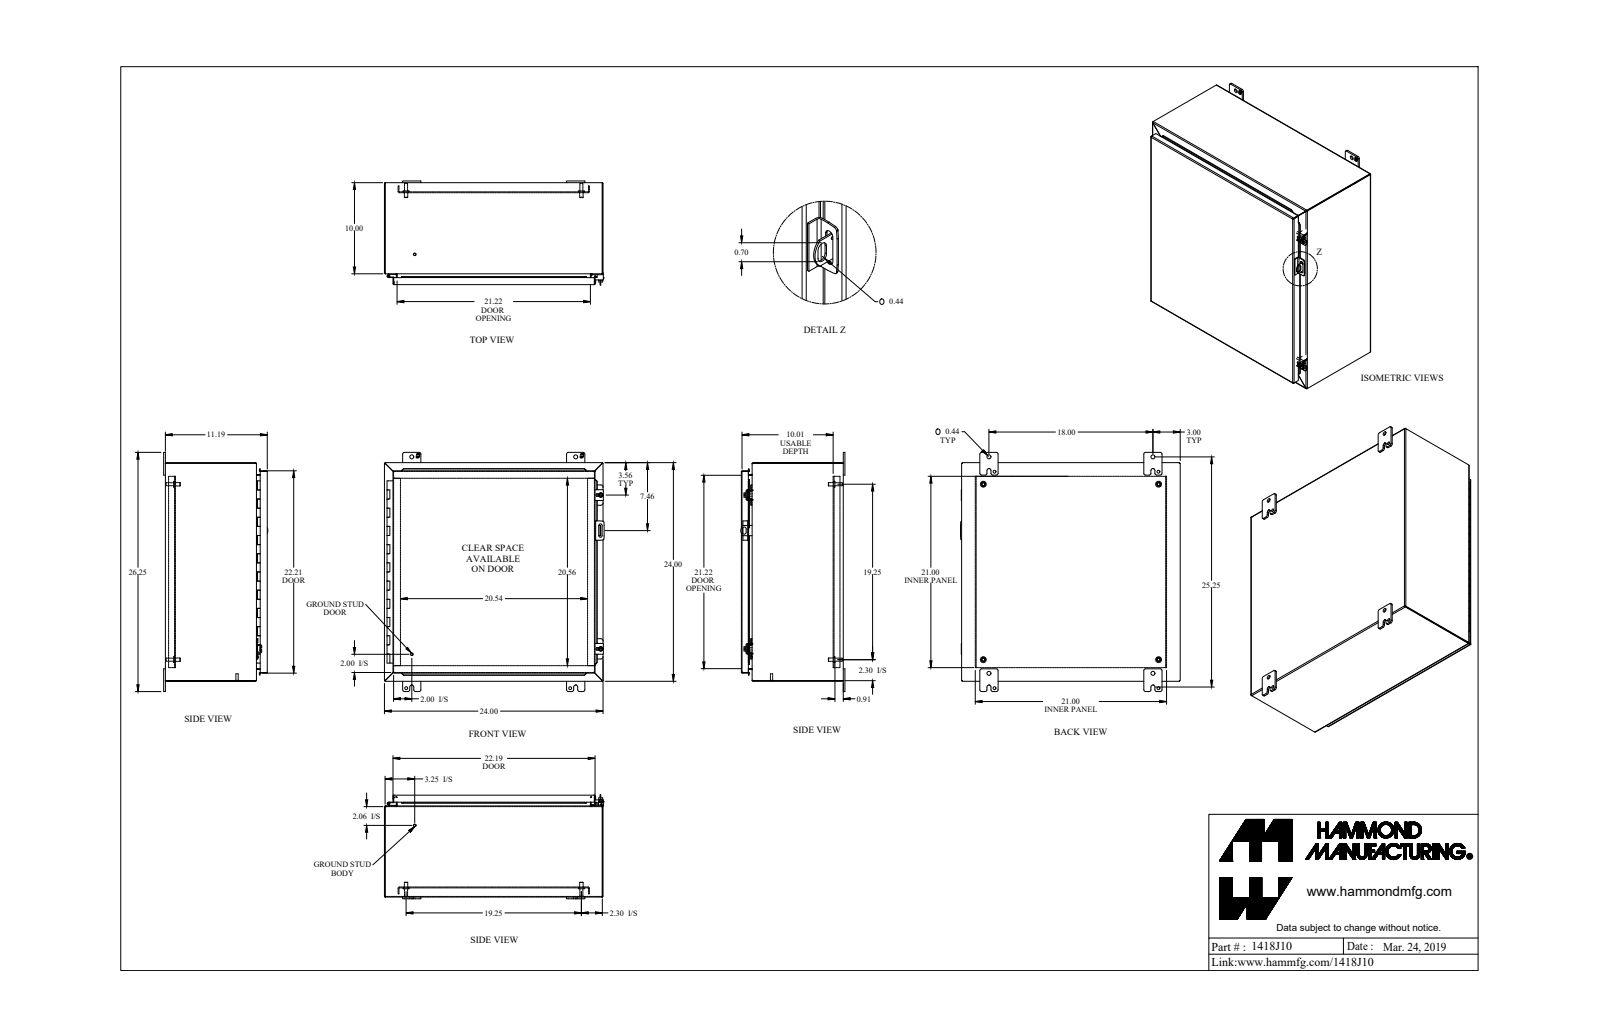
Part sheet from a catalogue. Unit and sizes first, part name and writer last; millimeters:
Units: millimetres
Overall size (bounding box): 666.8 × 612.8 × 290.5
Round holes (diameter × count): ⌀8 ×4, ⌀11.1 ×4, ⌀12.7 ×4, ⌀5.4 ×2, ⌀6.7 ×2, ⌀7.8 ×2, ⌀9.5 ×2, ⌀3.2 ×1, ⌀4.7 ×1, ⌀11.3 ×1, ⌀11.3 ×1
Round bosses / shafts (diameter × count): ⌀16.5 ×4, ⌀9.5 ×4, ⌀8.4 ×4, ⌀25.4 ×2, ⌀12.7 ×2, ⌀9.9 ×2, ⌀7.1 ×2, ⌀6.4 ×2
Partial cylindrical surfaces — rounded edges, fillets, slot ends (radius × count): R4.8 ×26, R0.9 ×20, R2.7 ×20, R1.2 ×13, R3.6 ×13, R1.1 ×8, R5.5 ×8, R6.4 ×8
Main face-to-face distances: 1.8, 282.3, 607.8, 280.4, 284.1, 23.8, 605.9, 609.6, 2.4, 25.6
Hole centre spacings: 489, 457.2, 44.1, 77.9, 565.4, 603.3, 691.5, 710.8
Volume: 3 805 000 mm³ · Surface area: 3 895 000 mm²
Bodies: 38 solids, 1010 faces (693 planar, 263 cylindrical, 54 other)
Part name (STEP PRODUCT): 1418J10
STEP written by: SolidWorks 2019 (AUTOMOTIVE_DESIGN)
